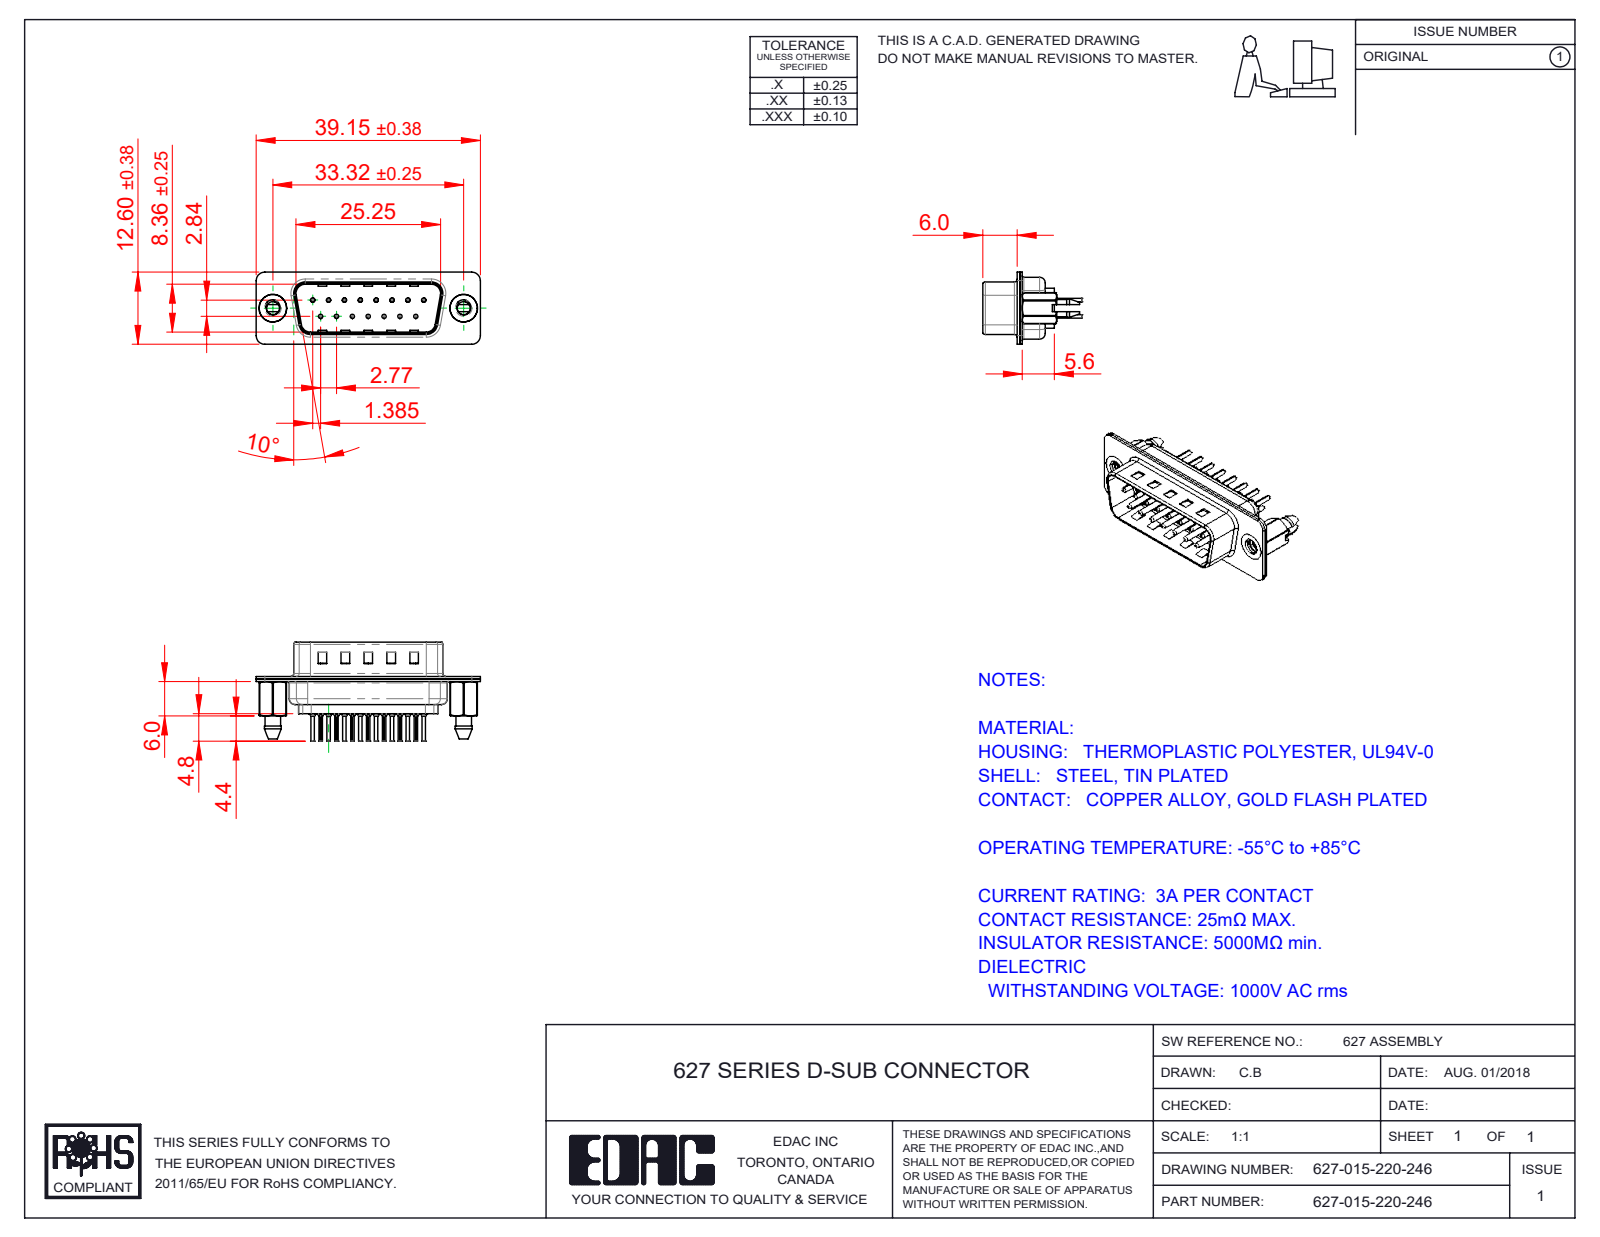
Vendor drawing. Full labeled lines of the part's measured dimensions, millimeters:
Part name (STEP PRODUCT): 627 4-40 Threaded Boardlock_LP; 627-015-220-046; 627 Contact Row 1_20L; 627 Shell Rear_15 Contacts (+3 more)
STEP written by: SolidWorks 2020 (CONFIG_CONTROL_DESIGN)
Units: millimetres
Bodies: 20 solids, 1884 faces (531 planar, 720 cylindrical, 633 other)
Overall size (bounding box): 39.15 × 17.3 × 12.6
Volume: 1 945 mm³ · Surface area: 5 684 mm²
Round holes (diameter × count): ⌀0.2 ×15, ⌀0.35 ×15, ⌀1.1 ×15, ⌀1.6 ×15, ⌀2.26 ×2, ⌀4 ×2, ⌀4.8 ×2
Round bosses / shafts (diameter × count): ⌀2 ×15, ⌀1.5 ×15, ⌀0.75 ×15, ⌀0.6 ×15, ⌀4.9 ×2
Partial cylindrical surfaces — rounded edges, fillets, slot ends (radius × count): R0.1 ×30, R1.5 ×18, R2 ×12, R1.6 ×10, R0.5 ×8, R0.25 ×4, R0.6 ×4, R0.65 ×4
Main face-to-face distances: 0.4, 0.45, 0.9, 0.82, 9.58, 8.76, 1.5, 1.4, 6.5, 5.6
Hole centre spacings: 3.16, 2.77, 5.54, 8.31, 11.08, 5.03, 5.04, 7.48
